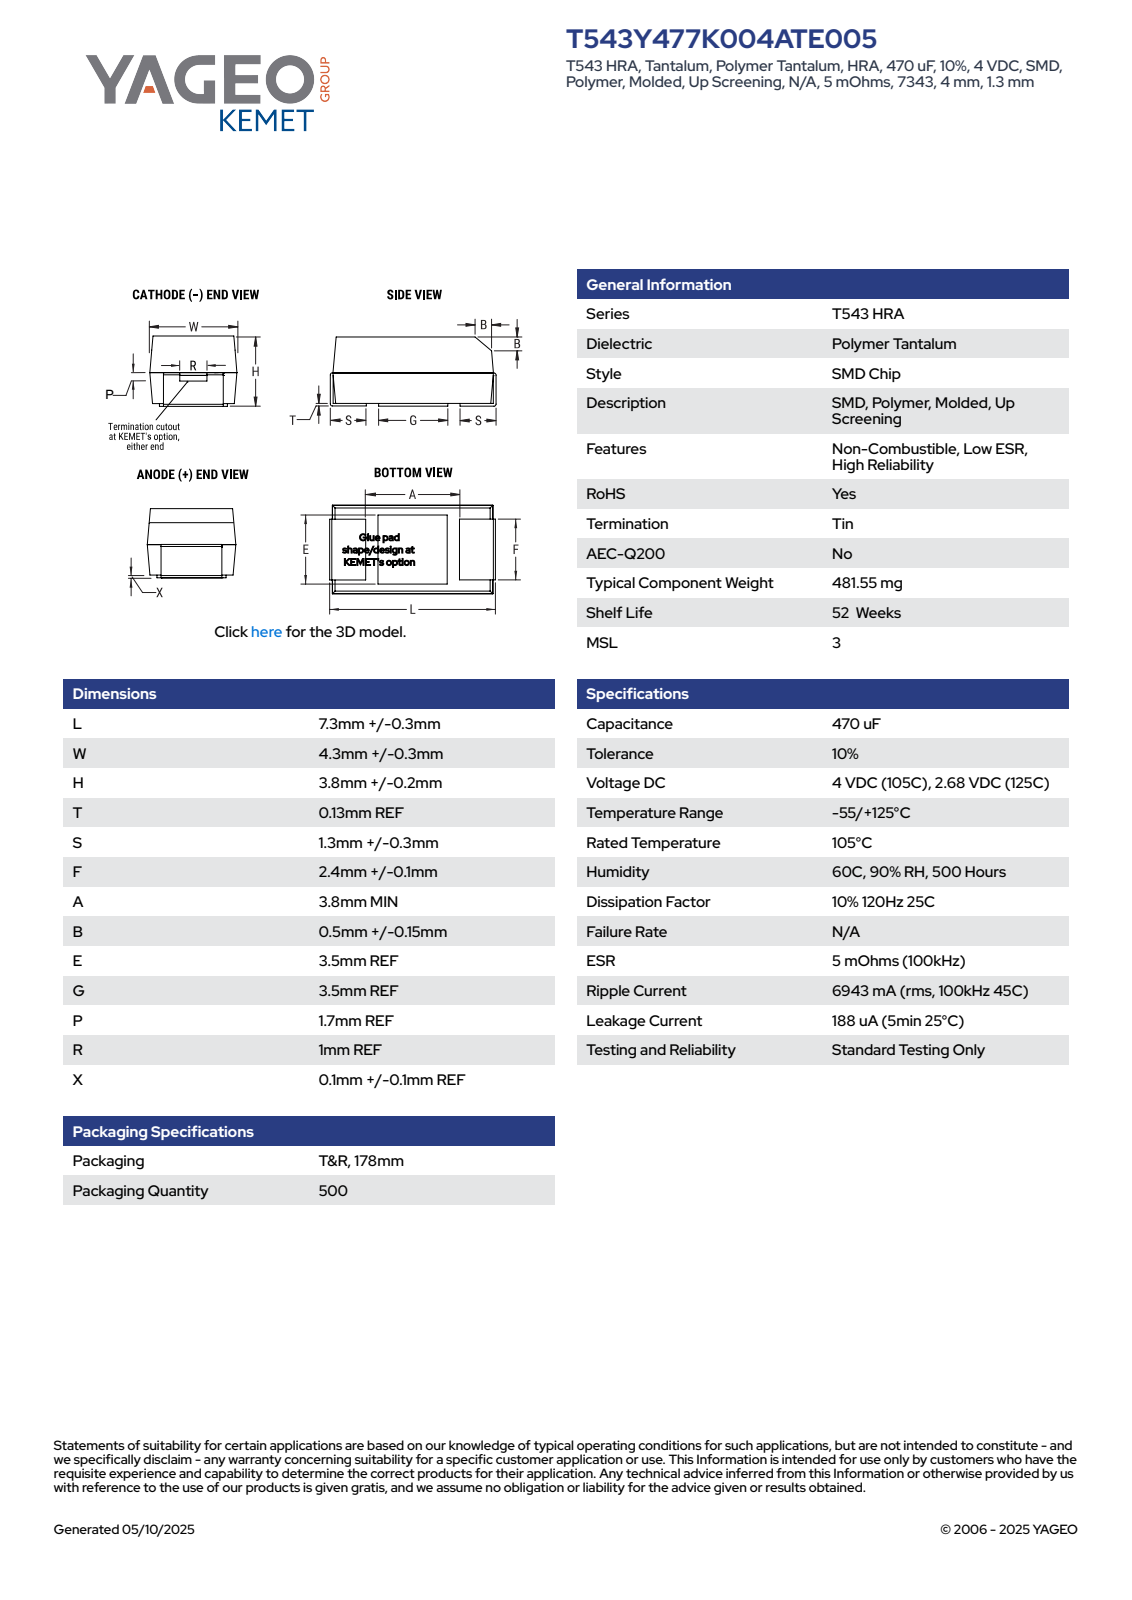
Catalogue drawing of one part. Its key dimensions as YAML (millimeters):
part_name: "CTSM_TCM2NK_7343_L7.6W4.6H4T0.13S1.3F2.5A3.8B0.65E3.5G3.5P1.7R1X0.2"
step_written_by: "SolidWorks 2020 (AUTOMOTIVE_DESIGN)"
units: millimeters
bodies: {solids: 4, faces: 100, planar: 95, cylindrical: 5, other: 0}
overall_size: [7.6, 4.6, 4]
volume: 121
surface_area: 178
partial_cylinders:
  - {radius: 0.1, count: 4}
face_to_face_distances: [4.56, 4, 3.8, 7.47, 3.87, 7.6, 7.34, 2.05, 5.55, 1.92]
